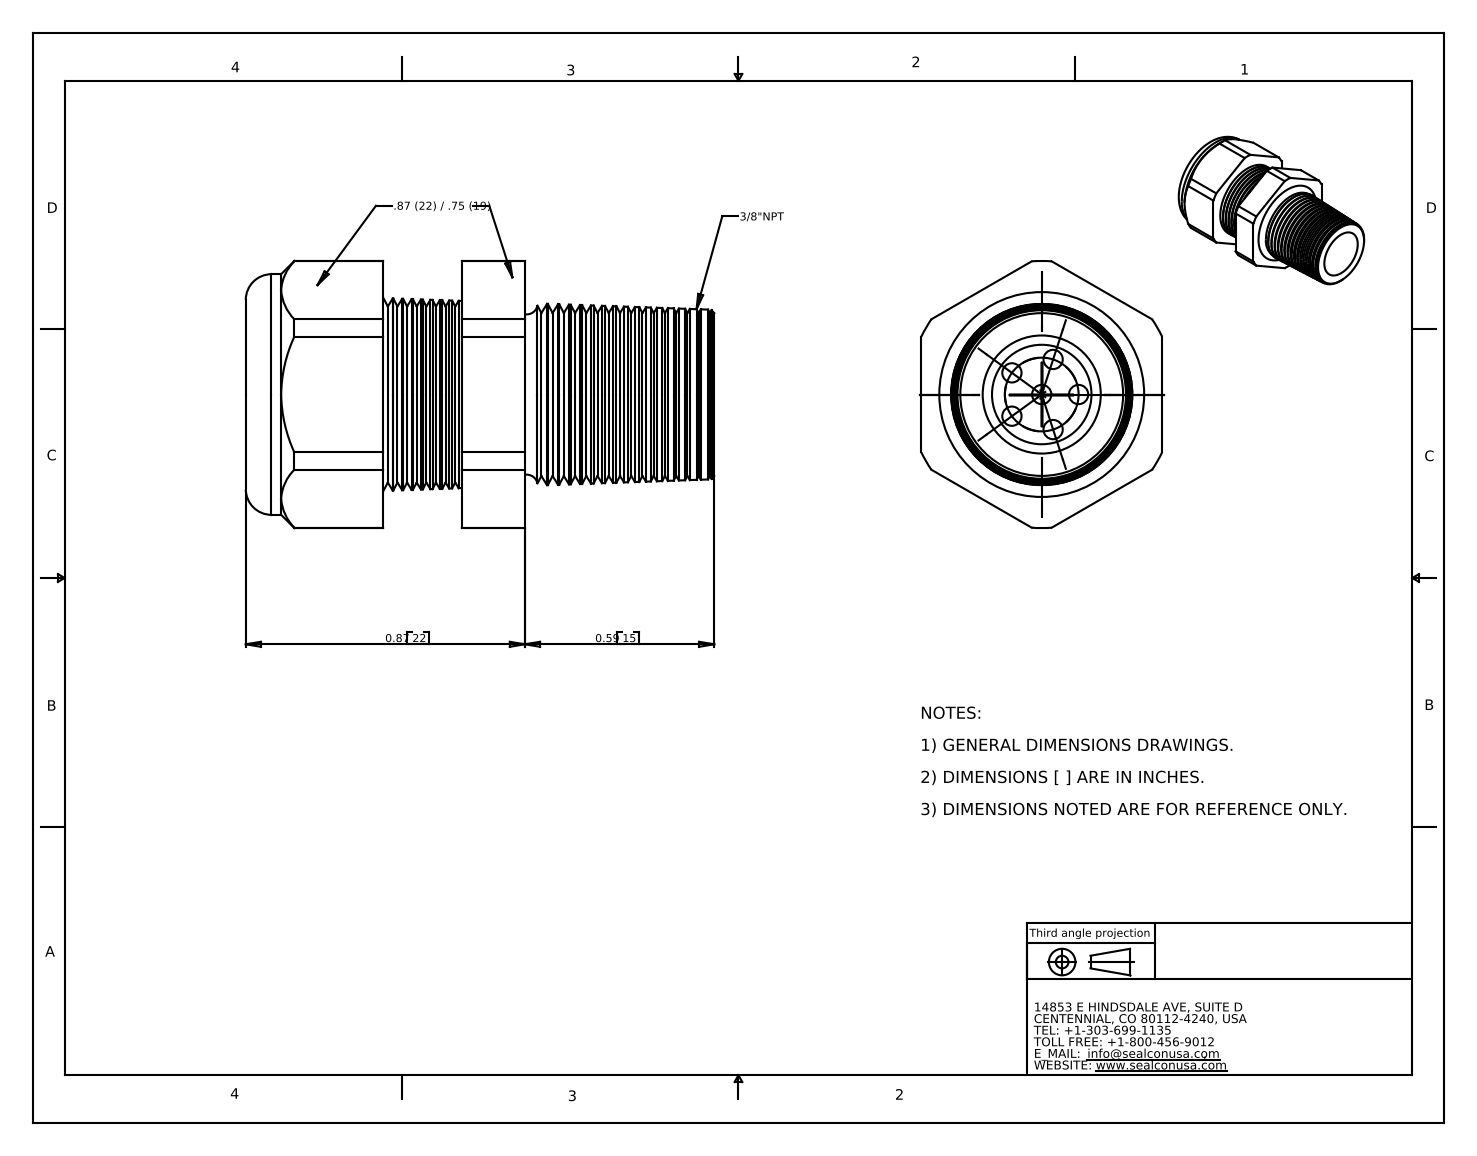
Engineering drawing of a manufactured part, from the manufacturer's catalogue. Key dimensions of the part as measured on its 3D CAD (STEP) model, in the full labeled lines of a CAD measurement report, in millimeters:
Part name (STEP PRODUCT): CD09N6-GY
STEP written by: SolidWorks 2007 (CONFIG_CONTROL_DESIGN)
Units: millimetres
Bodies: 2 solids, 210 faces (20 planar, 32 cylindrical, 158 other)
Overall size (bounding box): 37.1 × 21.2 × 19.1
Volume: 6 030 mm³ · Surface area: 4 561 mm²
Round holes (diameter × count): ⌀1.5 ×6, ⌀7.4 ×1, ⌀7.9 ×1
Round bosses / shafts (diameter × count): ⌀19.1 ×1
Partial cylindrical surfaces — rounded edges, fillets, slot ends (radius × count): R10.6 ×1
Main face-to-face distances: 19.1, 17.1, 10.9, 6.2, 19.1, 22.1, 11.2, 5, 37.1, 26.2
Hole centre spacings: 2.9, 3.4, 5.6, 3.4, 5.6
